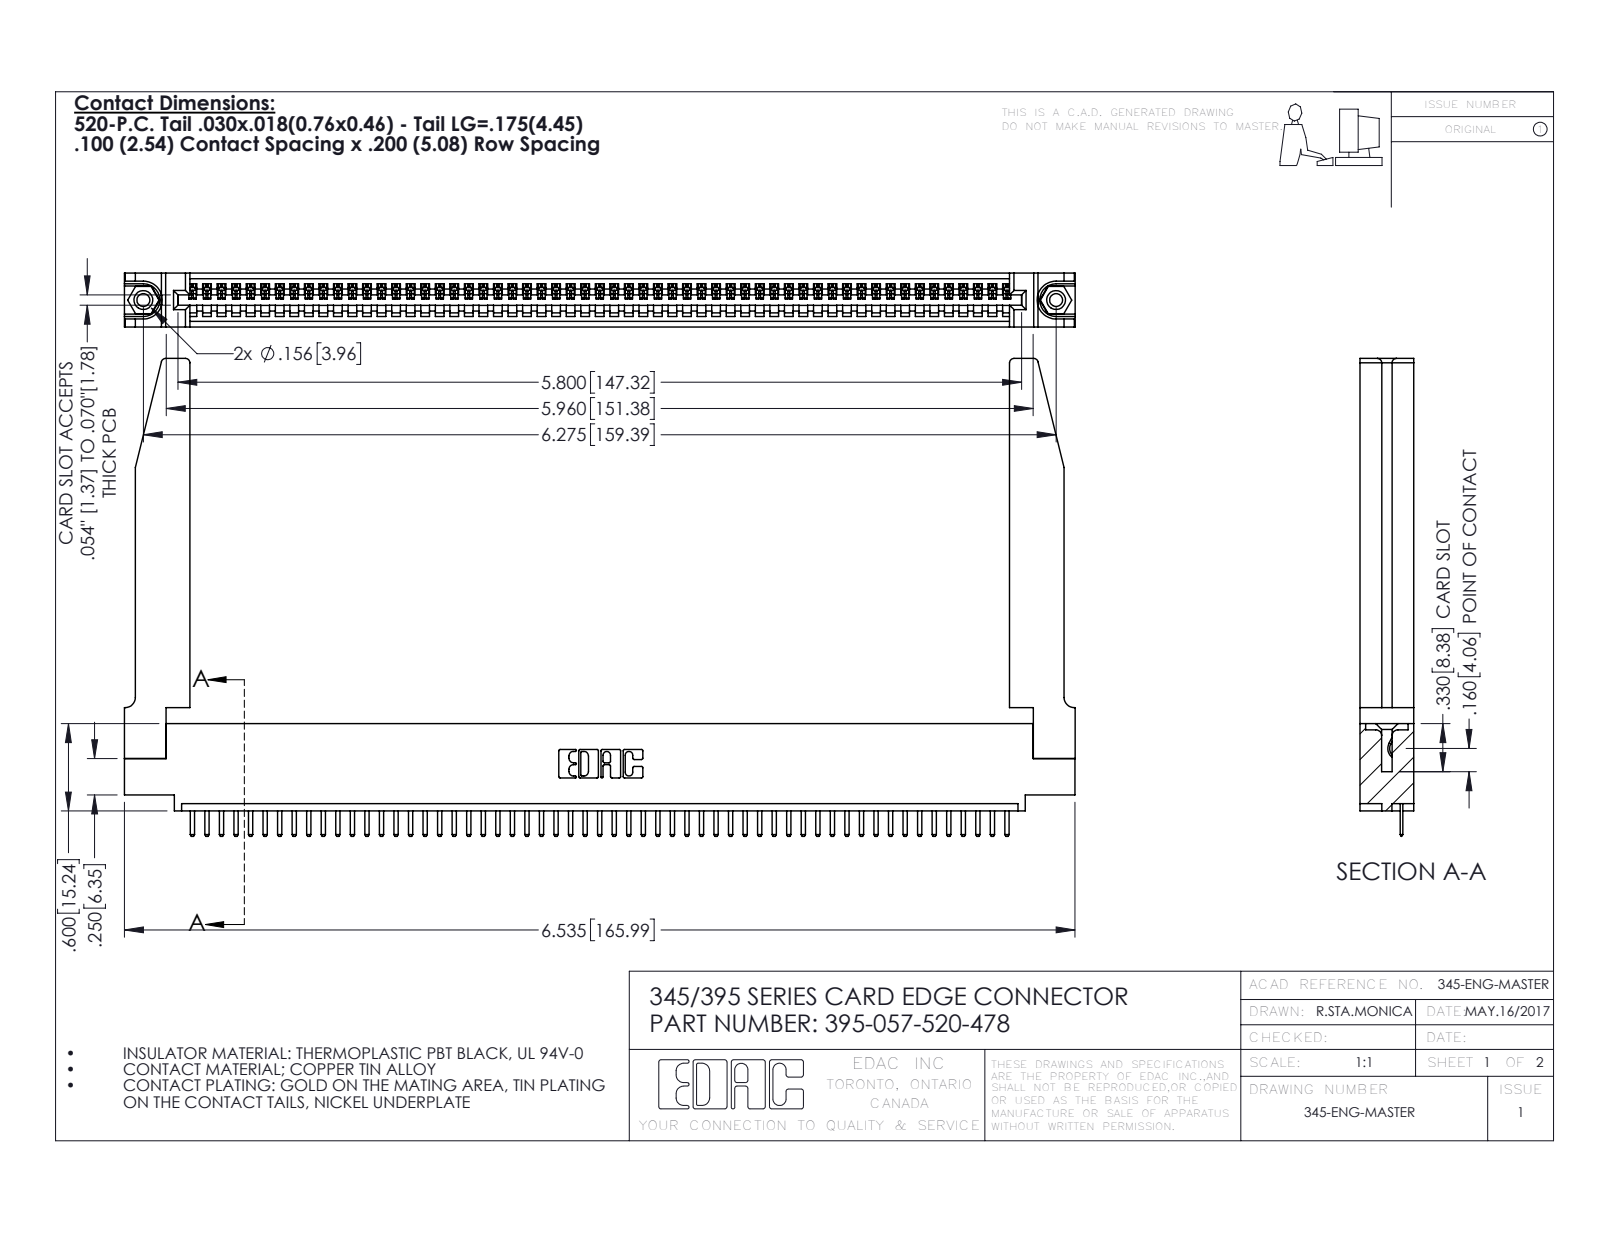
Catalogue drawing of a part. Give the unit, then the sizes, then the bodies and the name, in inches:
Units: inches
Overall size (bounding box): 6.536 × 3.285 × 0.37
Round holes (diameter × count): ⌀0.089 ×2, ⌀0.125 ×2, ⌀0.156 ×2, ⌀0.064 ×1
Round bosses / shafts (diameter × count): ⌀0.155 ×2
Partial cylindrical surfaces — rounded edges, fillets, slot ends (radius × count): R0.01 ×116, R0.006 ×114, R0.01 ×22, R0.03 ×8, R0.007 ×6, R0.031 ×6, R0.026 ×3, R0.031 ×2
Main face-to-face distances: 0.37, 0.072, 0.298, 0.2, 0.098, 0.272, 0.025, 0.225, 0.072, 0.148
Hole centre spacings: 0.27, 6.039, 6.275
Volume: 1.429 in³ · Surface area: 42.47 in²
Bodies: 62 solids, 3898 faces (2620 planar, 1226 cylindrical, 52 other)
Part name (STEP PRODUCT): 395-057-520-478; 345-292-001_345-293-120; 345-220-078_345-220-078; 345-250-001_345-250-001-102 (+1 more)
STEP written by: SolidWorks 2016 (CONFIG_CONTROL_DESIGN)
